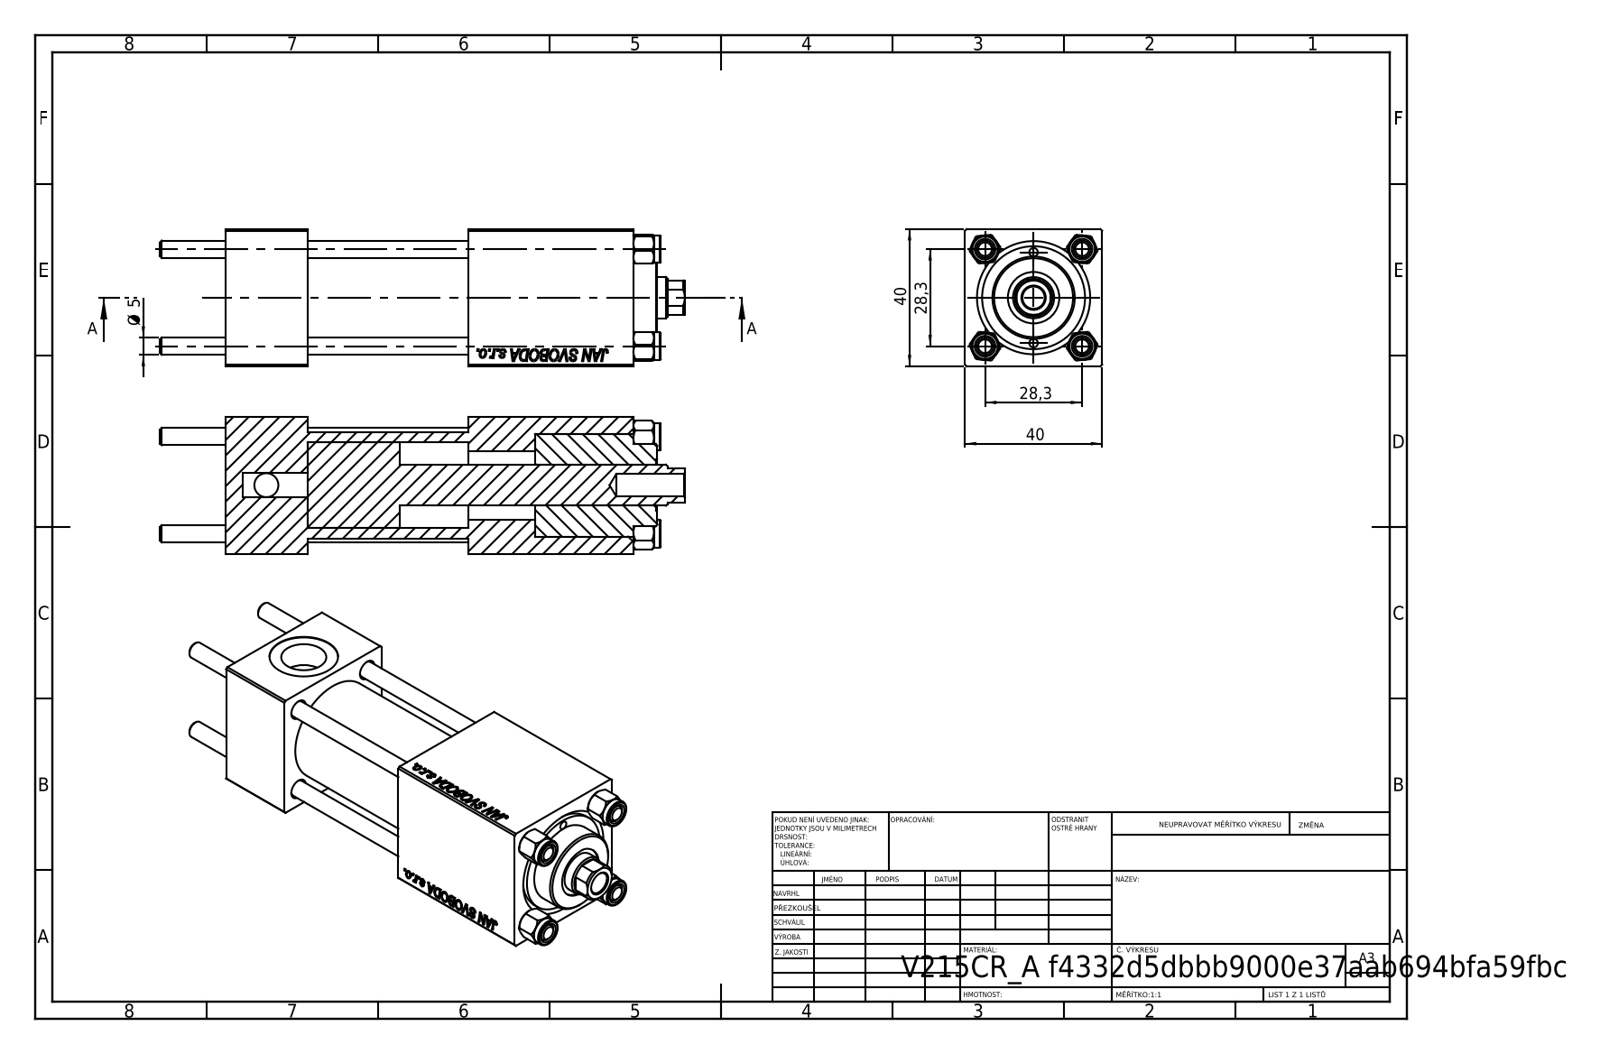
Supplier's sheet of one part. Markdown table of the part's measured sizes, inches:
| quantity | value |
| --- | --- |
| part name | NUT_M5; V215_VC_A; CR025_012_A_0_G_A_G_M_020_+#_##_TYCINKA; V215CR_BODY_A (+1 more) |
| STEP written by | SolidWorks 2019 (CONFIG_CONTROL_DESIGN) |
| units | inches |
| bodies | 11 solids, 1137 faces (519 planar, 82 cylindrical, 536 other) |
| overall size | 6.024 × 1.575 × 1.575 |
| volume | 8.85 in³ |
| surface area | 91.27 in² |
| round holes (diameter × count) | 0.197 × 4, 0.787 × 3, 0.098 × 2, 0.276 × 2, 0.518 × 2, 0.256 × 1, 0.472 × 1, 0.591 × 1, 0.984 × 1, 1.181 × 1 |
| round bosses / shafts (diameter × count) | 0.315 × 4, 1.22 × 1, 0.945 × 1 |
| partial cylindrical surfaces (radius × count) | 0.217 × 1 |
| main face-to-face distances | 1.575, 0.945, 3.555, 2.61, 4.685, 3.74, 1.13, 2.795, 1.85, 0.76 |
| hole center spacings | 0.558, 0.788, 1.114, 1.214, 0.522, 1.576, 1.043, 2.835 |
